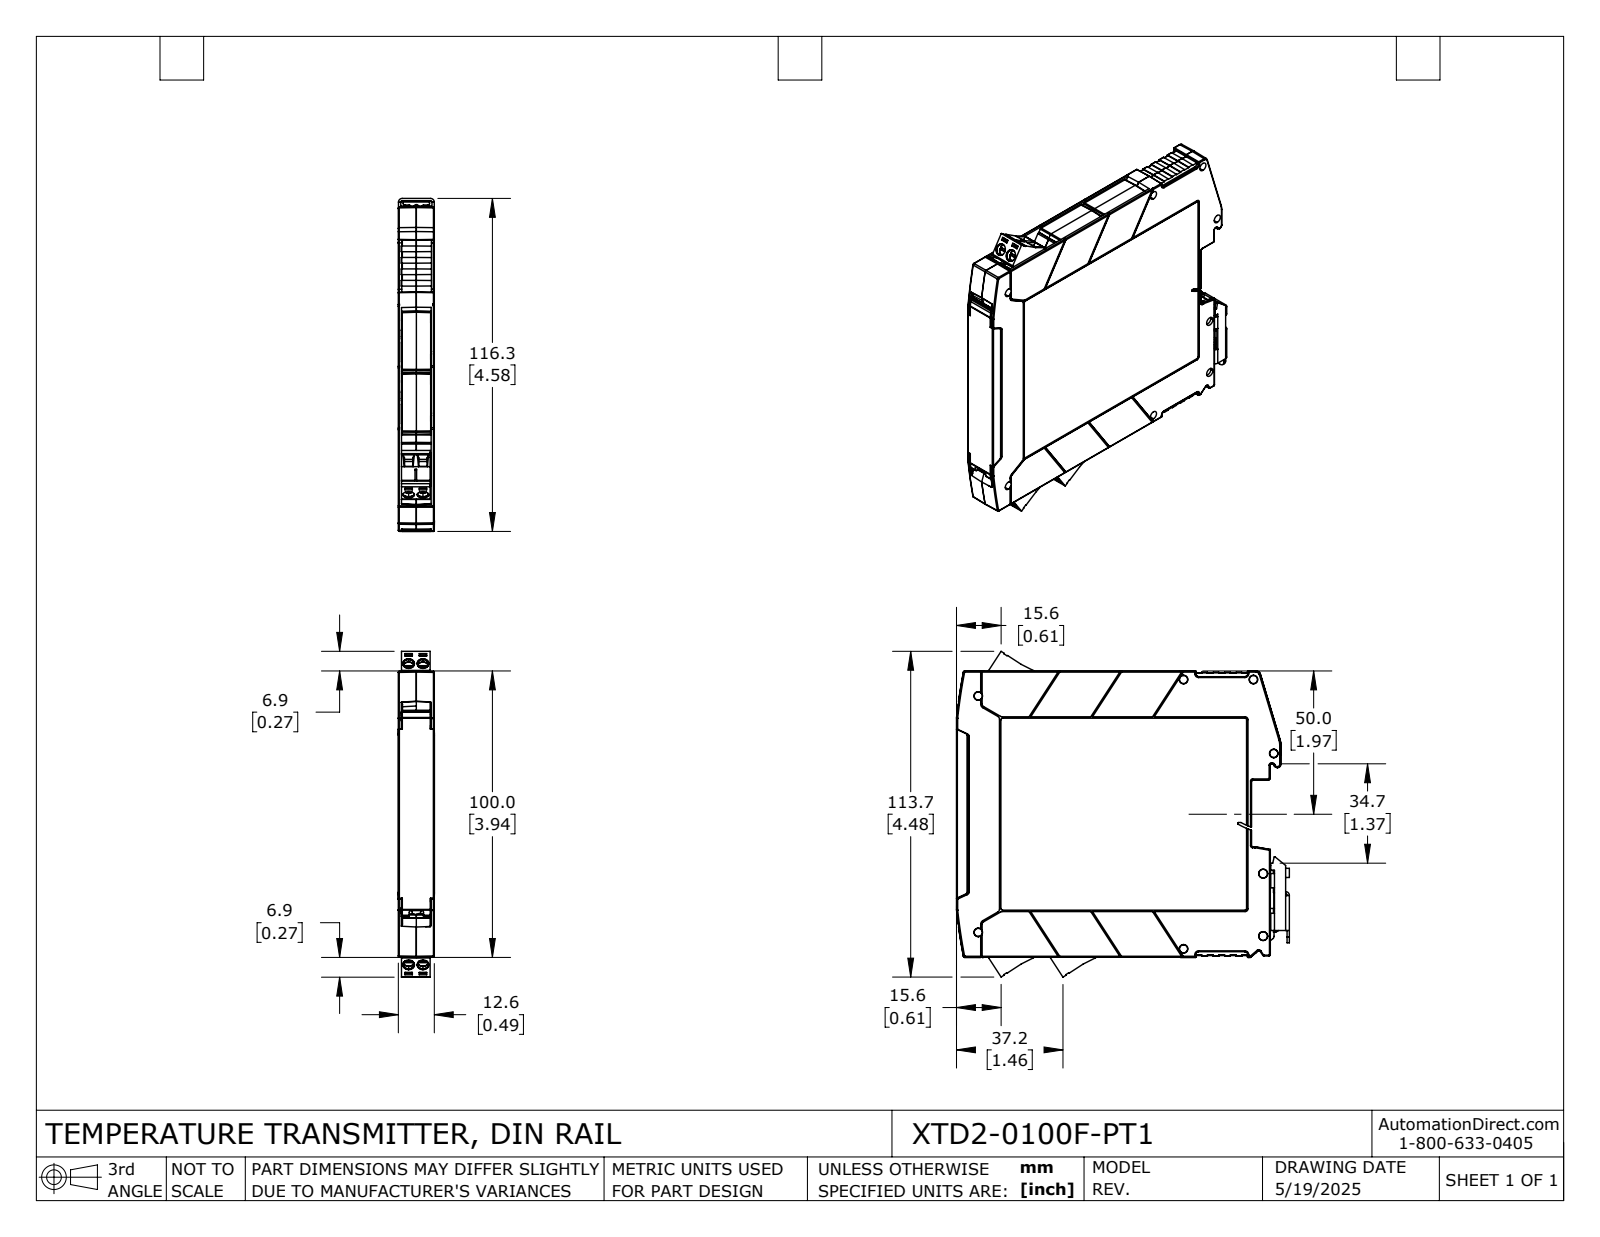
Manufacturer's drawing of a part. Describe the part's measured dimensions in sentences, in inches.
The part is named "XTD2-0100F-PT1". Its 3-D file was written by "SolidWorks 2024 (AUTOMOTIVE_DESIGN)". It is 14 solids with 3337 faces: 1910 planar, 596 cylindrical and 831 other. Overall it measures 4.577 by 4.478 by 0.496 inches. Its volume is 2.41 cubic inches and its surface area 101.5 square inches. Round holes: 6 of diameter 0.063, 6 of diameter 0.11, 6 of diameter 0.152, 6 of diameter 0.159. Round bosses or shafts: 6 of diameter 0.156, 6 of diameter 0.098, 2 of diameter 0.059, 2 of diameter 0.053. Partial cylindrical surfaces (rounded edges, fillets, slot ends): 89 of radius 0.008, 78 of radius 0.012, 71 of radius 0.02, 22 of radius 0.039, 20 of radius 0.004, 13 of radius 0.016, 12 of radius 0.006, 8 of radius 0.028. The main face-to-face distances are 0.049, 0.445, 0.494, 0.396, 0.043, 0.451, 0.402, 0.031, 0.198, 0.247. The hole center spacings are 0.197, 0.464, 0.504, 0.713, 0.739.
